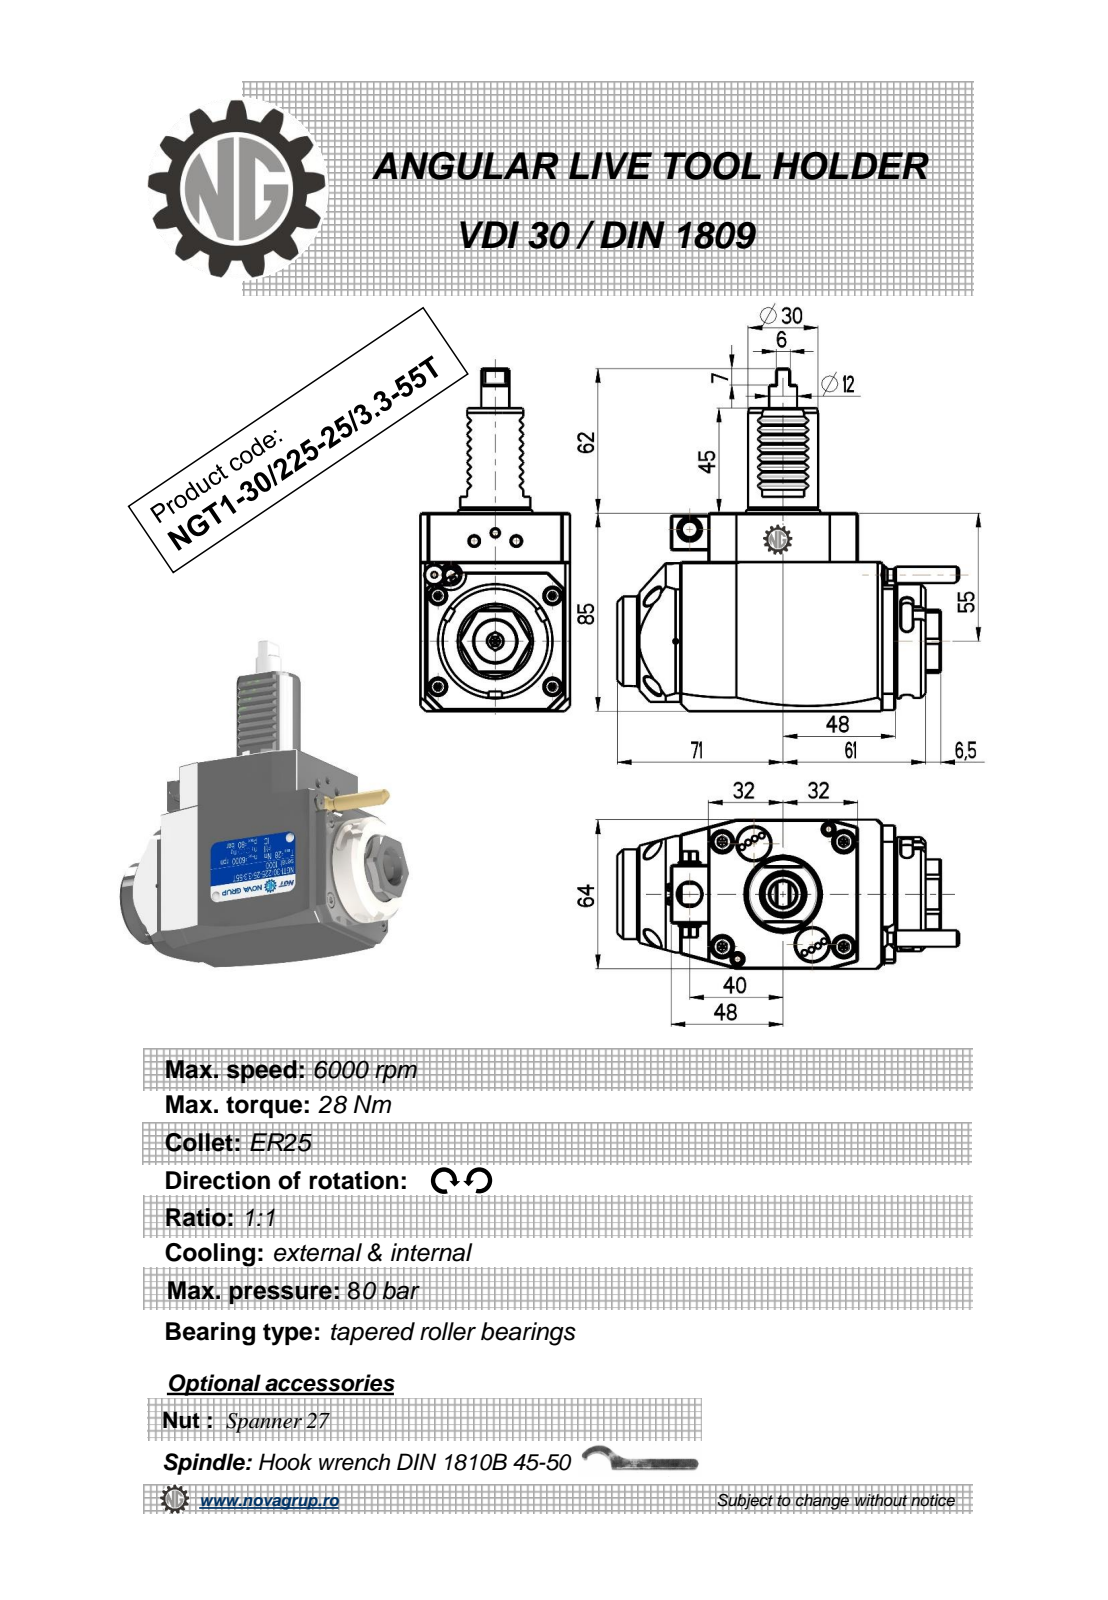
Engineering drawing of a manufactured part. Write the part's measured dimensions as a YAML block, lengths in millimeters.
part_name: "NGT1_30_225_25_3_3_55T"
step_written_by: "PRO/ENGINEER BY PARAMETRIC TECHNOLOGY CORPORATION, 2010280 (CONFIG_CONTROL_DESIGN)"
units: millimeters
bodies: {solids: 1, faces: 384, planar: 214, cylindrical: 94, other: 76}
overall_size: [147, 146.38, 64]
volume: 557199
surface_area: 50088
round_holes:
  - {diameter: 2.5, count: 1}
  - {diameter: 3, count: 1}
  - {diameter: 9.5, count: 1}
  - {diameter: 10, count: 1}
  - {diameter: 18, count: 1}
round_bosses_or_shafts:
  - {diameter: 8, count: 2}
  - {diameter: 49, count: 1}
  - {diameter: 42, count: 1}
  - {diameter: 38.5, count: 1}
  - {diameter: 30, count: 1}
  - {diameter: 12, count: 1}
  - {diameter: 10, count: 1}
  - {diameter: 7, count: 1}
partial_cylinders:
  - {radius: 0.3, count: 16}
  - {radius: 2.5, count: 6}
  - {radius: 0.8, count: 2}
  - {radius: 180, count: 2}
  - {radius: 3.85, count: 1}
  - {radius: 4.25, count: 1}
  - {radius: 4.5, count: 1}
  - {radius: 15, count: 1}
face_to_face_distances: [64, 85, 16, 80, 13, 21, 29, 2.83, 0.5, 20]
hole_center_spacings: [26.17, 34.25, 46.5]
